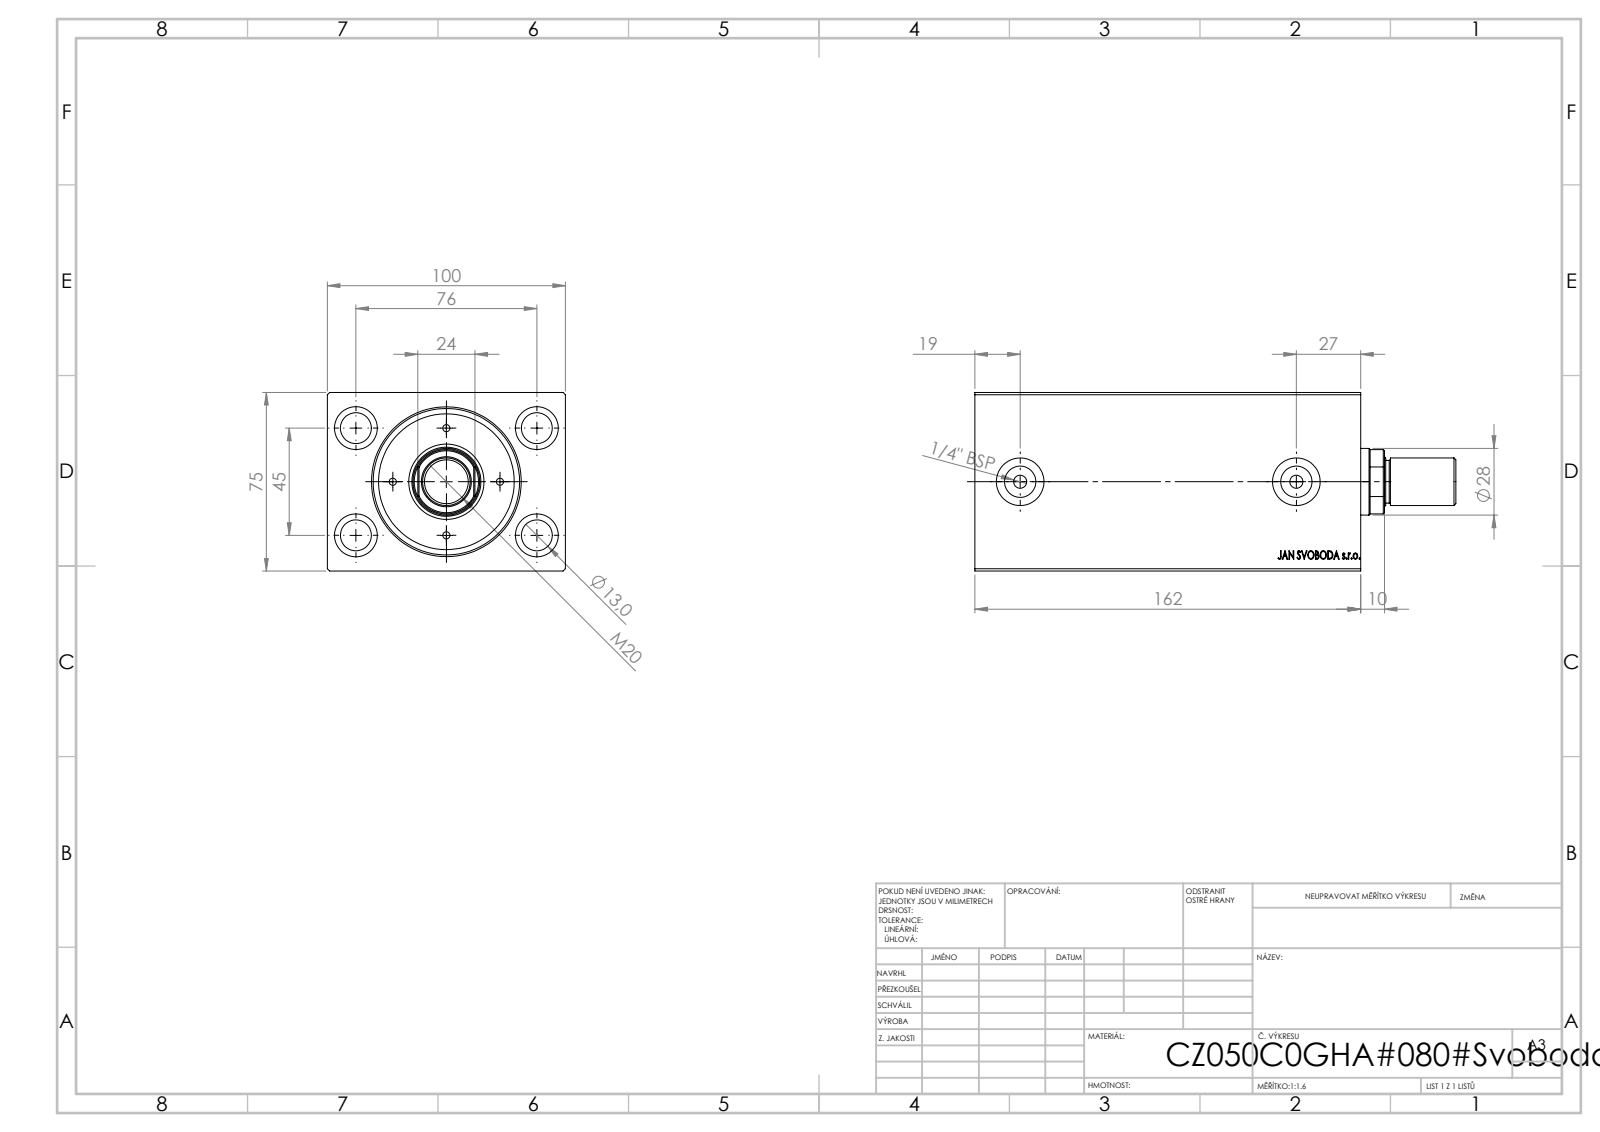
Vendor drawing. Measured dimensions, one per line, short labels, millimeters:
written by: SolidWorks 2019 (CONFIG_CONTROL_DESIGN)
unit: mm
bodies: 1 solid, 825 faces (397 planar, 46 cylindrical, 382 other)
size: 162 × 100 × 75
volume: 820 967 mm³; area: 122 545 mm²
holes: 4× ⌀13, 4× ⌀18, 2× ⌀5.5, 2× ⌀8, 2× ⌀13.16, 2× ⌀20, 1× ⌀36, 1× ⌀50, 1× ⌀61.5
face distances: 75, 100, 162, 144.2, 17.8, 161.8, 17.6, 10, 134.2, 151.8
hole spacings: 44.16, 45, 76, 88.32, 96, 116
